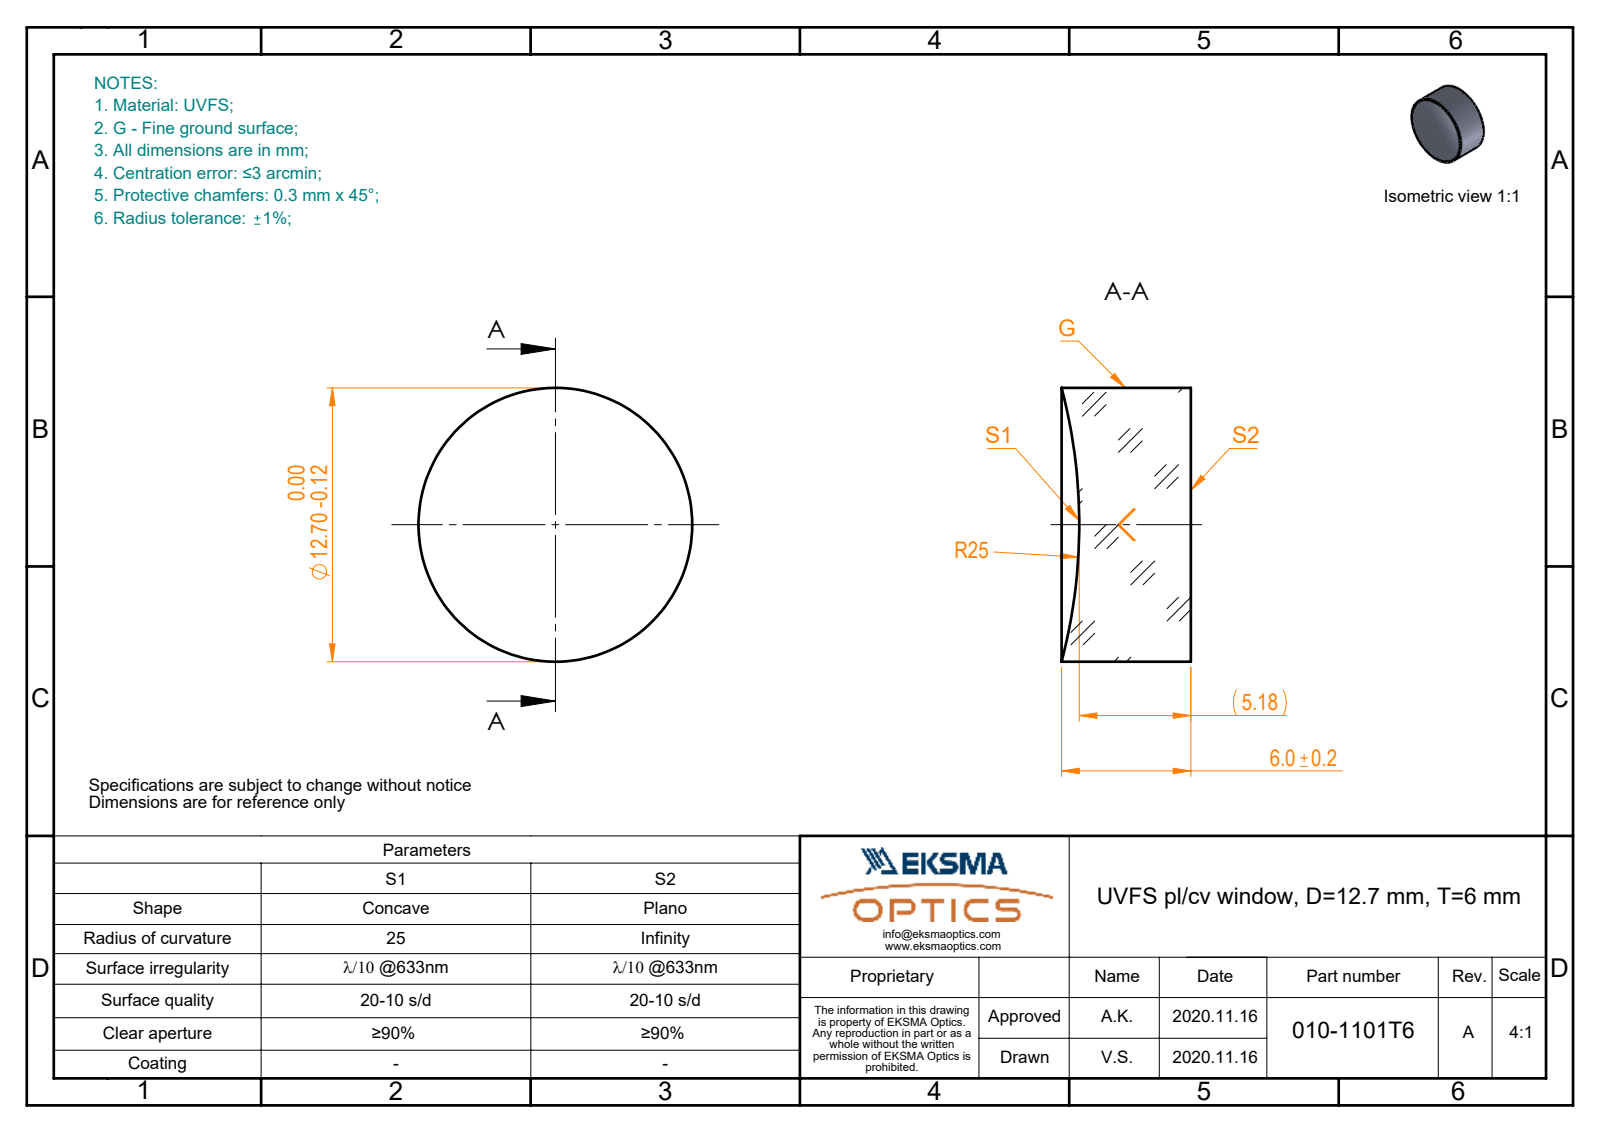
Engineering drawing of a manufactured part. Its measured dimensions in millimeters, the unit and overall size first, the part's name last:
Units: millimetres
Overall size (bounding box): 12.7 × 12.7 × 6
Round bosses / shafts (diameter × count): ⌀12.7 ×1
Volume: 708 mm³ · Surface area: 495 mm²
Bodies: 1 solid, 5 faces (1 planar, 2 cylindrical, 2 other)
Part name (STEP PRODUCT): 010-1101T6_UVFS_PCV_window
STEP written by: SolidWorks 2019 (CONFIG_CONTROL_DESIGN)
